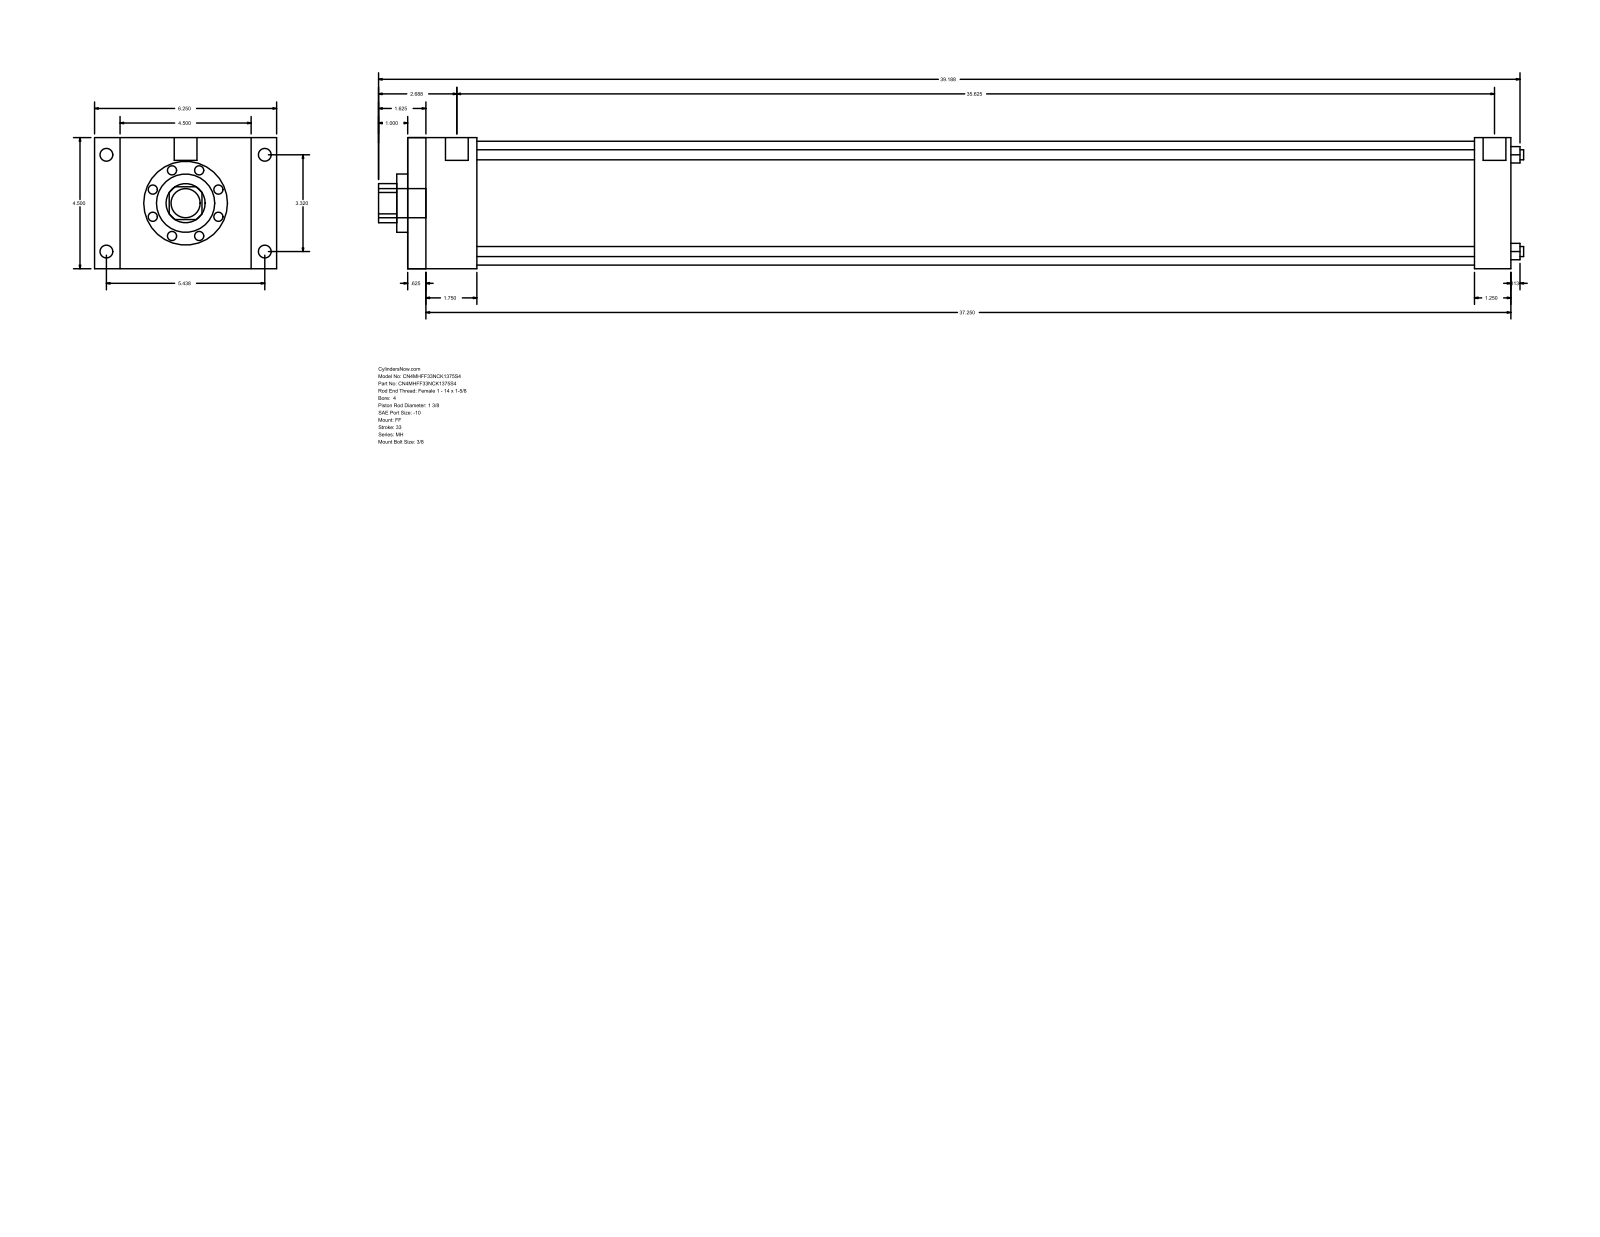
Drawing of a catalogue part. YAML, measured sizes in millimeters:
part_name: "MH_FF__0400_1.375"
step_written_by: "GSSL Pune (CONFIG_CONTROL_DESIGN)"
units: millimeters
bodies: {solids: 0, faces: 92, planar: 64, cylindrical: 28, other: 0}
overall_size: [998.54, 158.75, 114.3]
round_holes:
  - {diameter: 8.76, count: 4}
  - {diameter: 34.92, count: 1}
  - {diameter: 50.8, count: 1}
  - {diameter: 107.95, count: 1}
round_bosses_or_shafts:
  - {diameter: 11.13, count: 4}
  - {diameter: 8.73, count: 4}
  - {diameter: 19.84, count: 2}
  - {diameter: 25.4, count: 1}
partial_cylinders:
  - {radius: 17.06, count: 1}
face_to_face_distances: [114.3, 962.02, 15.87, 946.15, 60.32, 44.45, 901.7, 930.27, 914.4, 869.95]
hole_center_spacings: [59.62, 84.32, 119.25]
